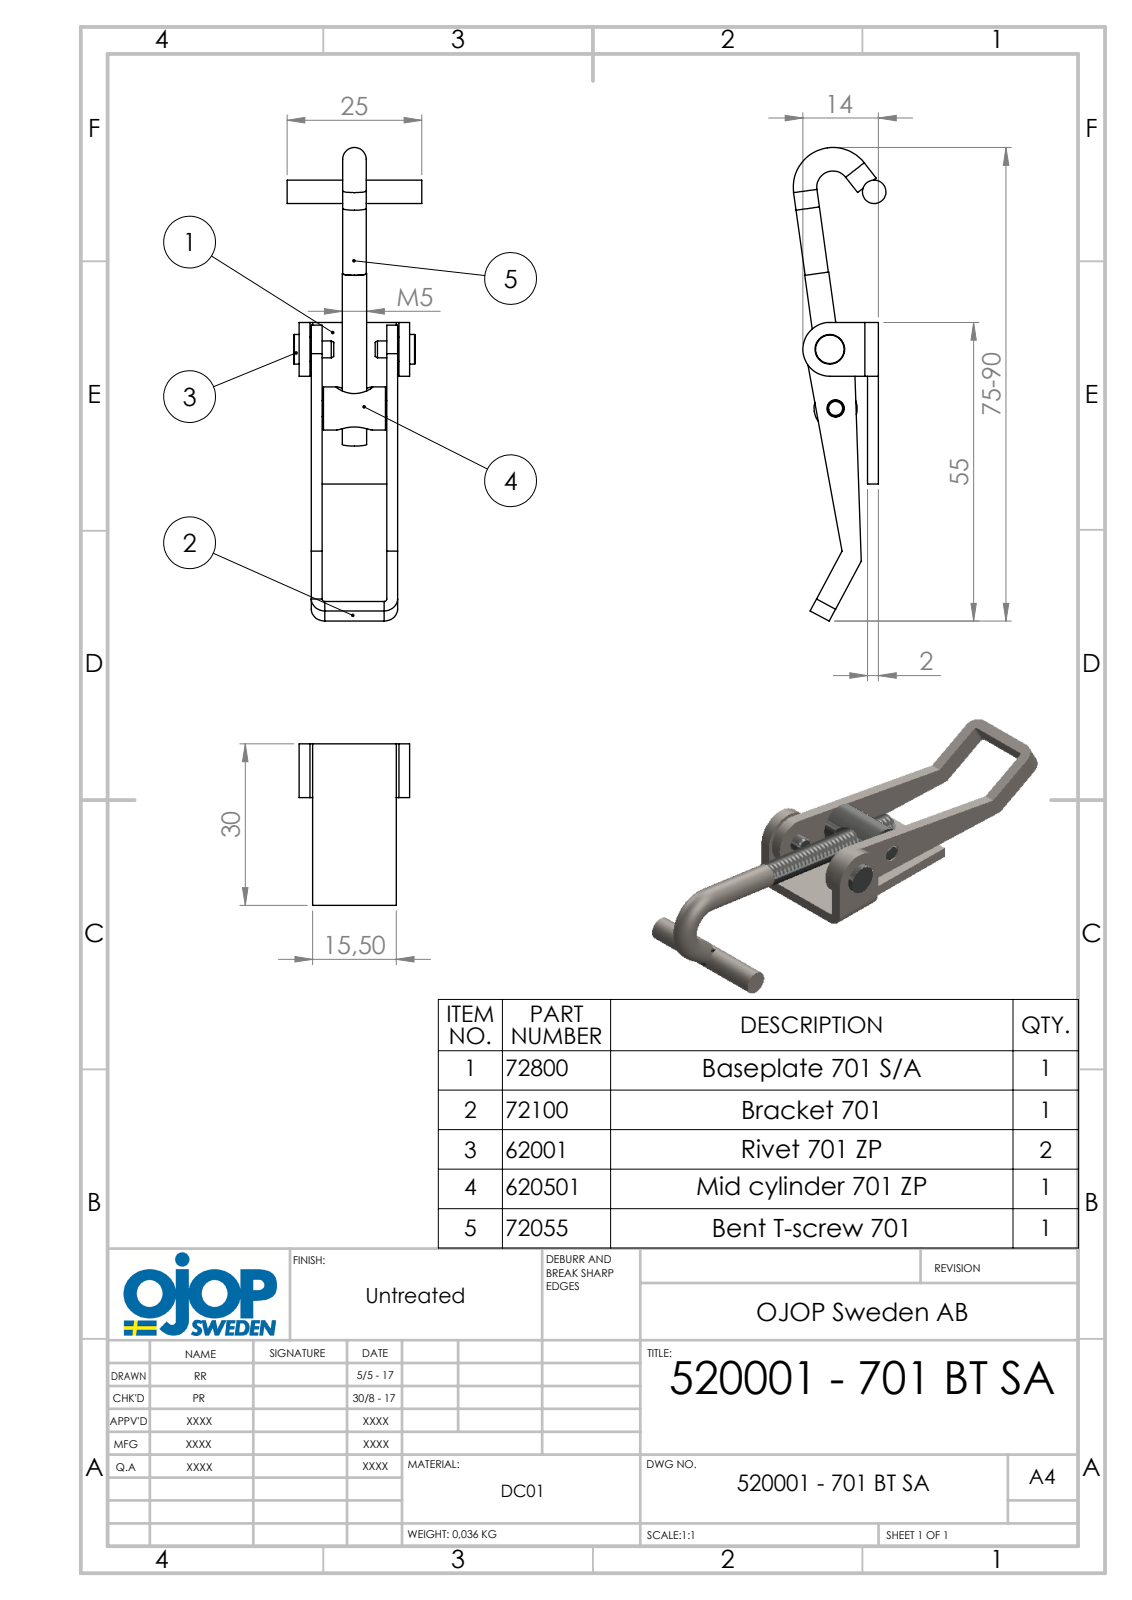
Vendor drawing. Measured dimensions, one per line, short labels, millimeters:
name: Böjd T-skruv M5_Default<As Machined>; 520001 - 701 BTSA; 701 - SA; 701 - Ansatsnit (+2 more)
written by: SolidWorks 2015 (AUTOMOTIVE_DESIGN)
unit: mm
bodies: 6 solids, 126 faces (53 planar, 55 cylindrical, 18 other)
size: 88.6 × 25 × 17.85
volume: 4 991 mm³; area: 5 779 mm²
holes: 2× ⌀3.2, 1× ⌀4.5, 1× ⌀4.8
bosses: 2× ⌀5, 1× ⌀8, 1× ⌀5.5, 1× ⌀5.01, 1× ⌀4.38, 1× ⌀3.15, 1× ⌀3
rounds: 4× R0.5, 4× R2.5, 1× R4.5, 1× R5
face distances: 2, 14, 2.25, 16, 16.25, 12, 4.25, 18.25, 18.5, 14.25
hole spacings: 11.02
